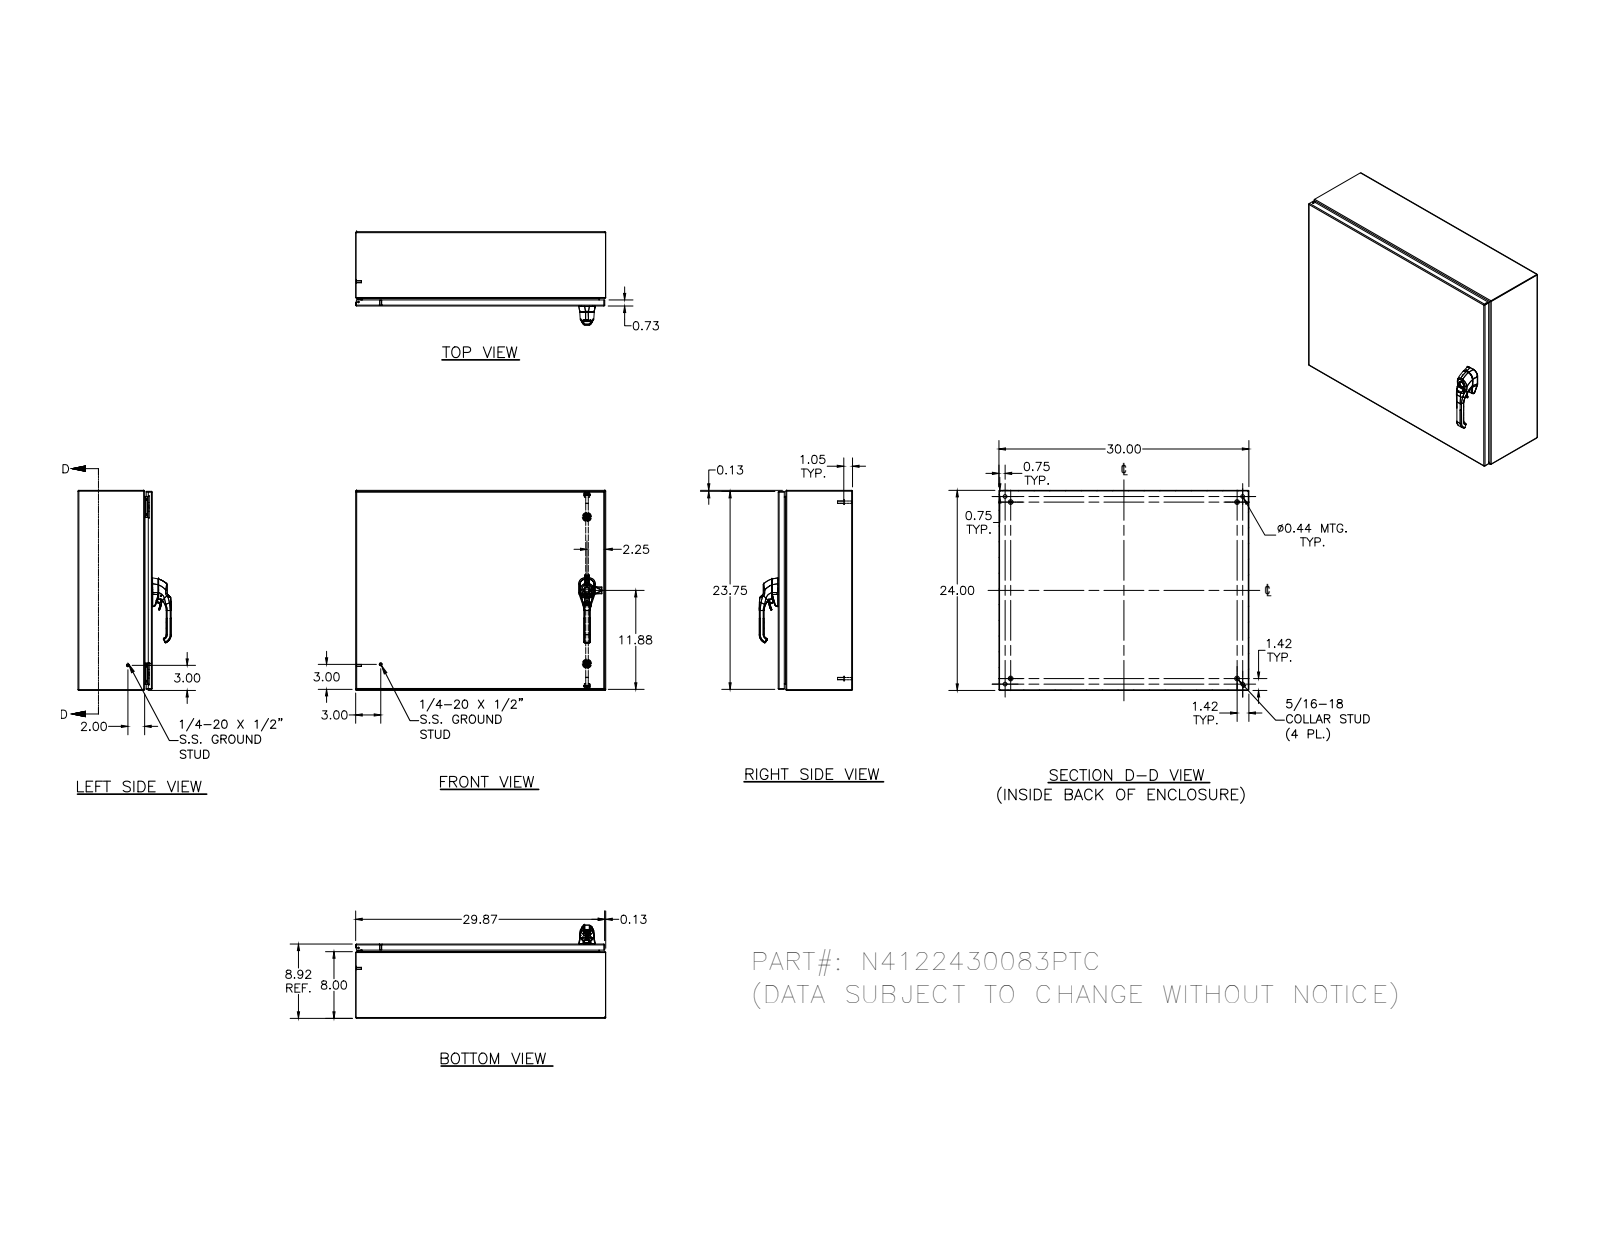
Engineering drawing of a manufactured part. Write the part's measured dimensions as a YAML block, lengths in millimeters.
part_name: "N4122430083PTC; N4122430083PTCBKP; N41224303PTCLID; HFW328176 (+8 more)"
step_written_by: "Autodesk Inventor 2011 (AUTOMOTIVE_DESIGN)"
units: millimeters
bodies: {solids: 49, faces: 2962, planar: 941, cylindrical: 1101, other: 920}
overall_size: [762, 609.6, 284.1]
volume: 3102000
surface_area: 3355000
round_holes:
  - {diameter: 4.8, count: 5}
  - {diameter: 2.4, count: 4}
  - {diameter: 3.9, count: 4}
  - {diameter: 4.2, count: 4}
  - {diameter: 4.2, count: 4}
  - {diameter: 4.4, count: 4}
  - {diameter: 5, count: 4}
  - {diameter: 11.1, count: 4}
  - {diameter: 5.4, count: 3}
  - {diameter: 6, count: 3}
  - {diameter: 9, count: 3}
  - {diameter: 2.7, count: 2}
round_bosses_or_shafts:
  - {diameter: 6.4, count: 10}
  - {diameter: 14.3, count: 4}
  - {diameter: 9.1, count: 4}
  - {diameter: 8.1, count: 4}
  - {diameter: 7.6, count: 4}
  - {diameter: 7, count: 4}
  - {diameter: 6.5, count: 4}
  - {diameter: 6, count: 4}
partial_cylinders:
  - {radius: 0.5, count: 203}
  - {radius: 0.3, count: 80}
  - {radius: 3, count: 33}
  - {radius: 0.8, count: 30}
  - {radius: 1.3, count: 26}
  - {radius: 0.5, count: 22}
  - {radius: 2.7, count: 20}
  - {radius: 0.4, count: 18}
face_to_face_distances: [1.9, 224.6, 226.5, 222.7, 607.7, 760.1, 609.6, 605.8, 758.2, 762]
hole_center_spacings: [507.9, 695.8, 0.4, 16.8, 524.7, 0.5, 4.5, 12.7]
